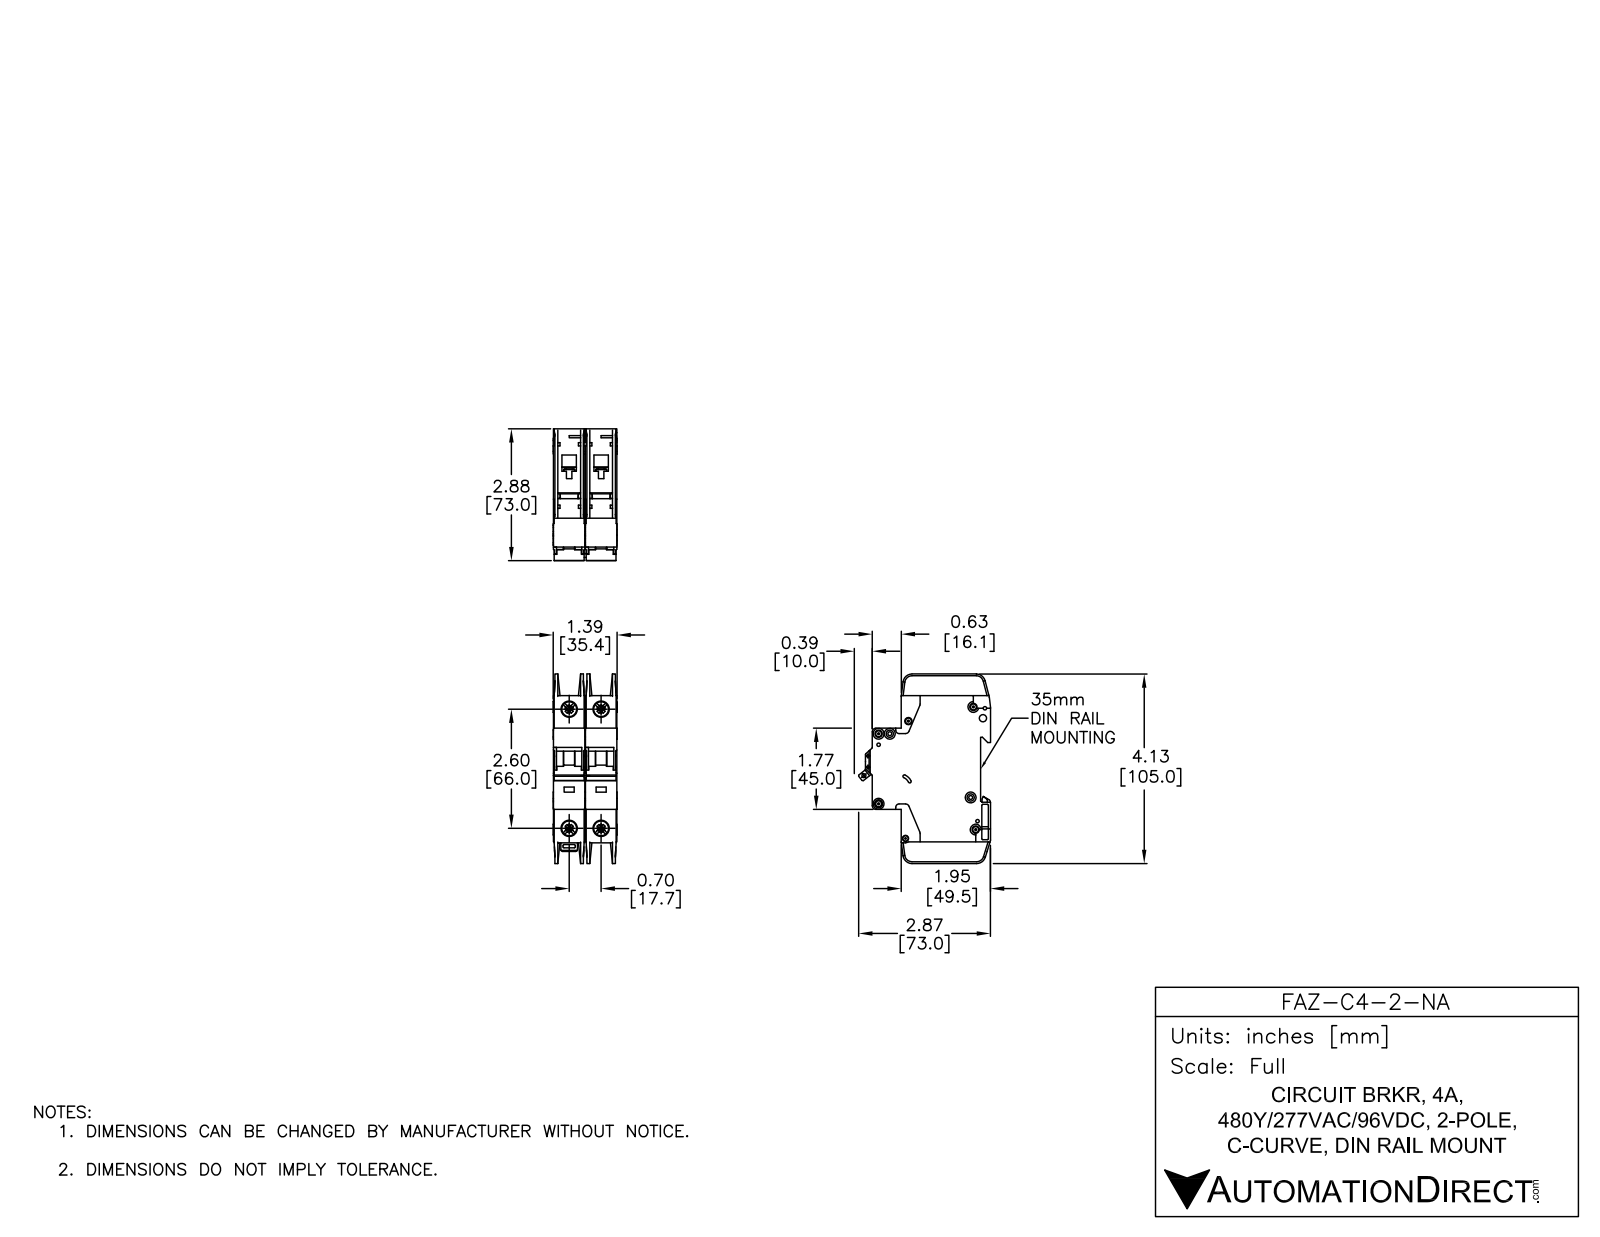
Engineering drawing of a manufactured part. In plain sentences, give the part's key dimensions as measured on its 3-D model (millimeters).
The part is named "FAZ-C4-2-NA". Its 3-D file was written by "SolidWorks 2014 (AUTOMOTIVE_DESIGN)". It is 6 solids with 1568 faces: 818 planar, 526 cylindrical and 224 other. Overall it measures 105 by 73.04 by 35.4 millimeters. Its volume is 155 390 cubic millimeters and its surface area 49 479 square millimeters. Round holes: 7 of diameter 3.6, 4 of diameter 7.15, 4 of diameter 8.2, 2 of diameter 1.09, 2 of diameter 1.5, 2 of diameter 4, 1 of diameter 1.9, 1 of diameter 2.15, 1 of diameter 2.2, 1 of diameter 2.55, 1 of diameter 3.3, 1 of diameter 3.4. Round bosses or shafts: 7 of diameter 6, 2 of diameter 2.5. Partial cylindrical surfaces (rounded edges, fillets, slot ends): 47 of radius 0.25, 24 of radius 0.5, 18 of radius 1, 12 of radius 2, 5 of radius 5, 4 of radius 1.8, 4 of radius 4, 2 of radius 0.2. The main face-to-face distances are 17.7, 17.5, 0.7, 15.05, 2.45, 1.75, 15.75, 13.3, 35.2, 17. The hole center spacings are 6.2, 17.7, 66, 68.33, 5.19, 6.1, 8.19, 8.56.
